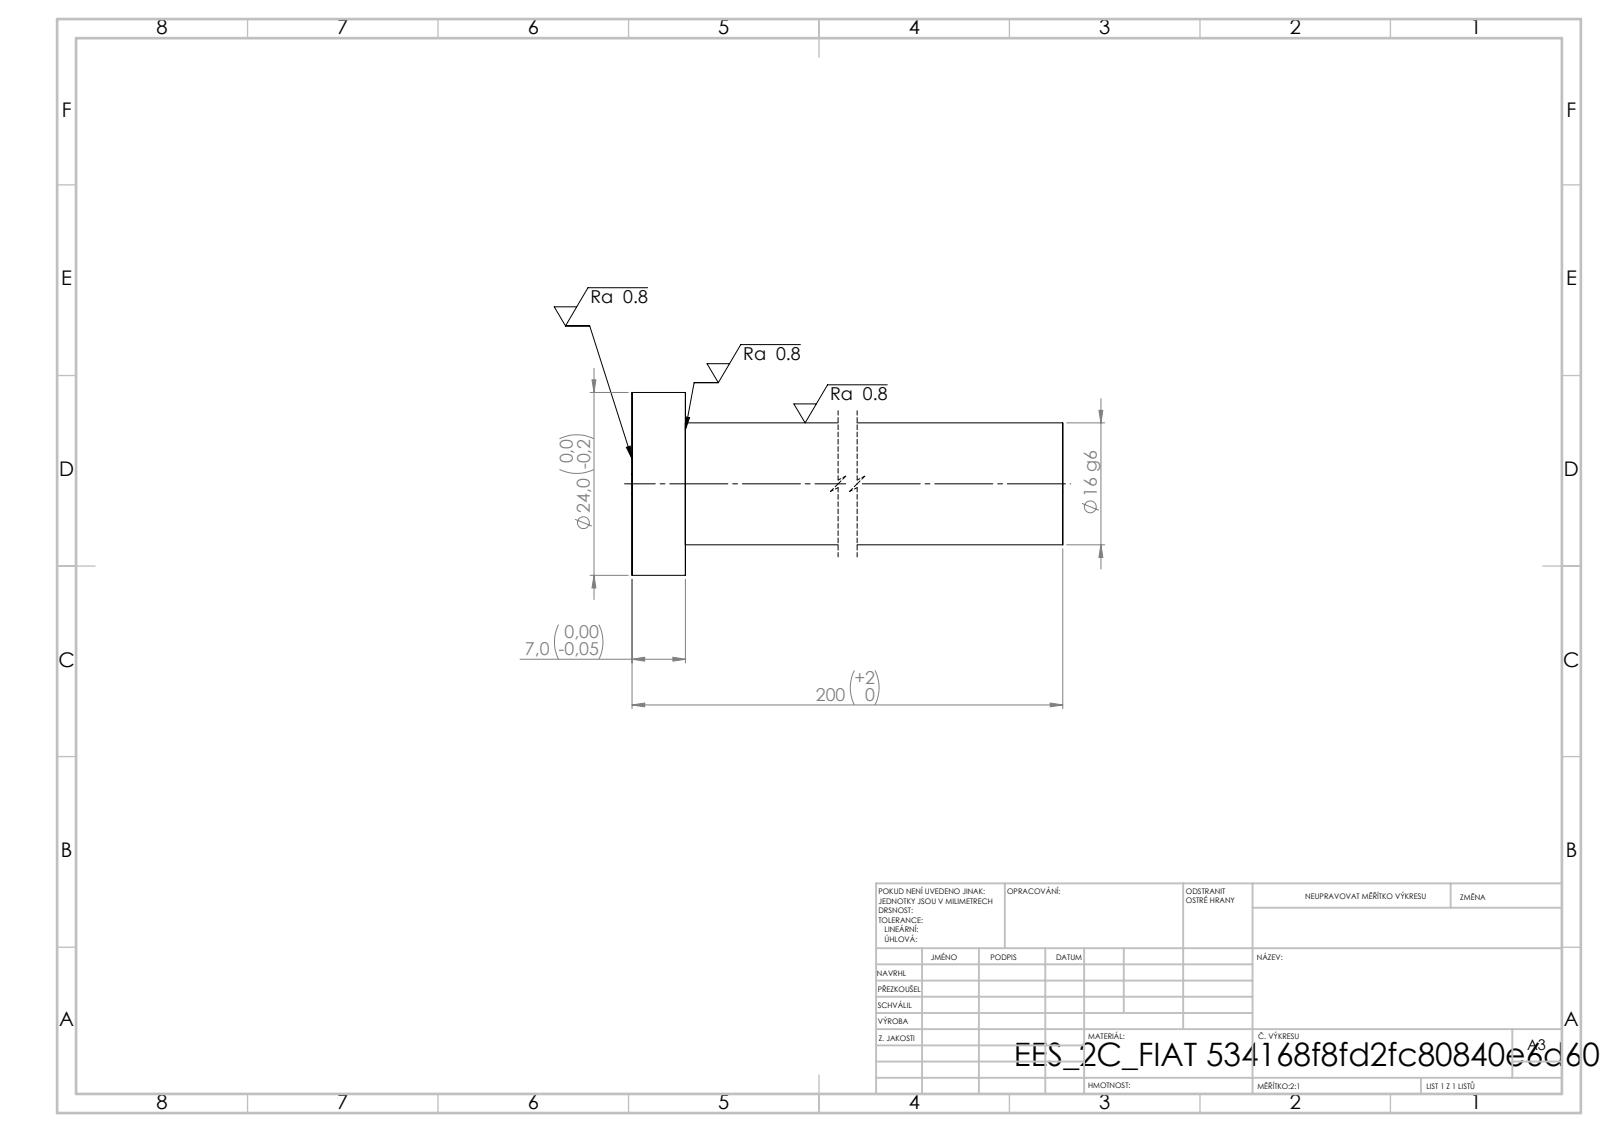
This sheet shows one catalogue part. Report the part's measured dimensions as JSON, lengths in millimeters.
{"step_written_by": "SolidWorks 2019 (CONFIG_CONTROL_DESIGN)", "units": "millimeters", "bodies": {"solids": 1, "faces": 7, "planar": 3, "cylindrical": 4, "other": 0}, "overall_size": [200, 24, 24], "volume_mm3": 41972, "surface_area_mm2": 11134, "round_bosses_or_shafts": [[24, 1], [16, 1]], "face_to_face_distances": [7, 200, 193]}
